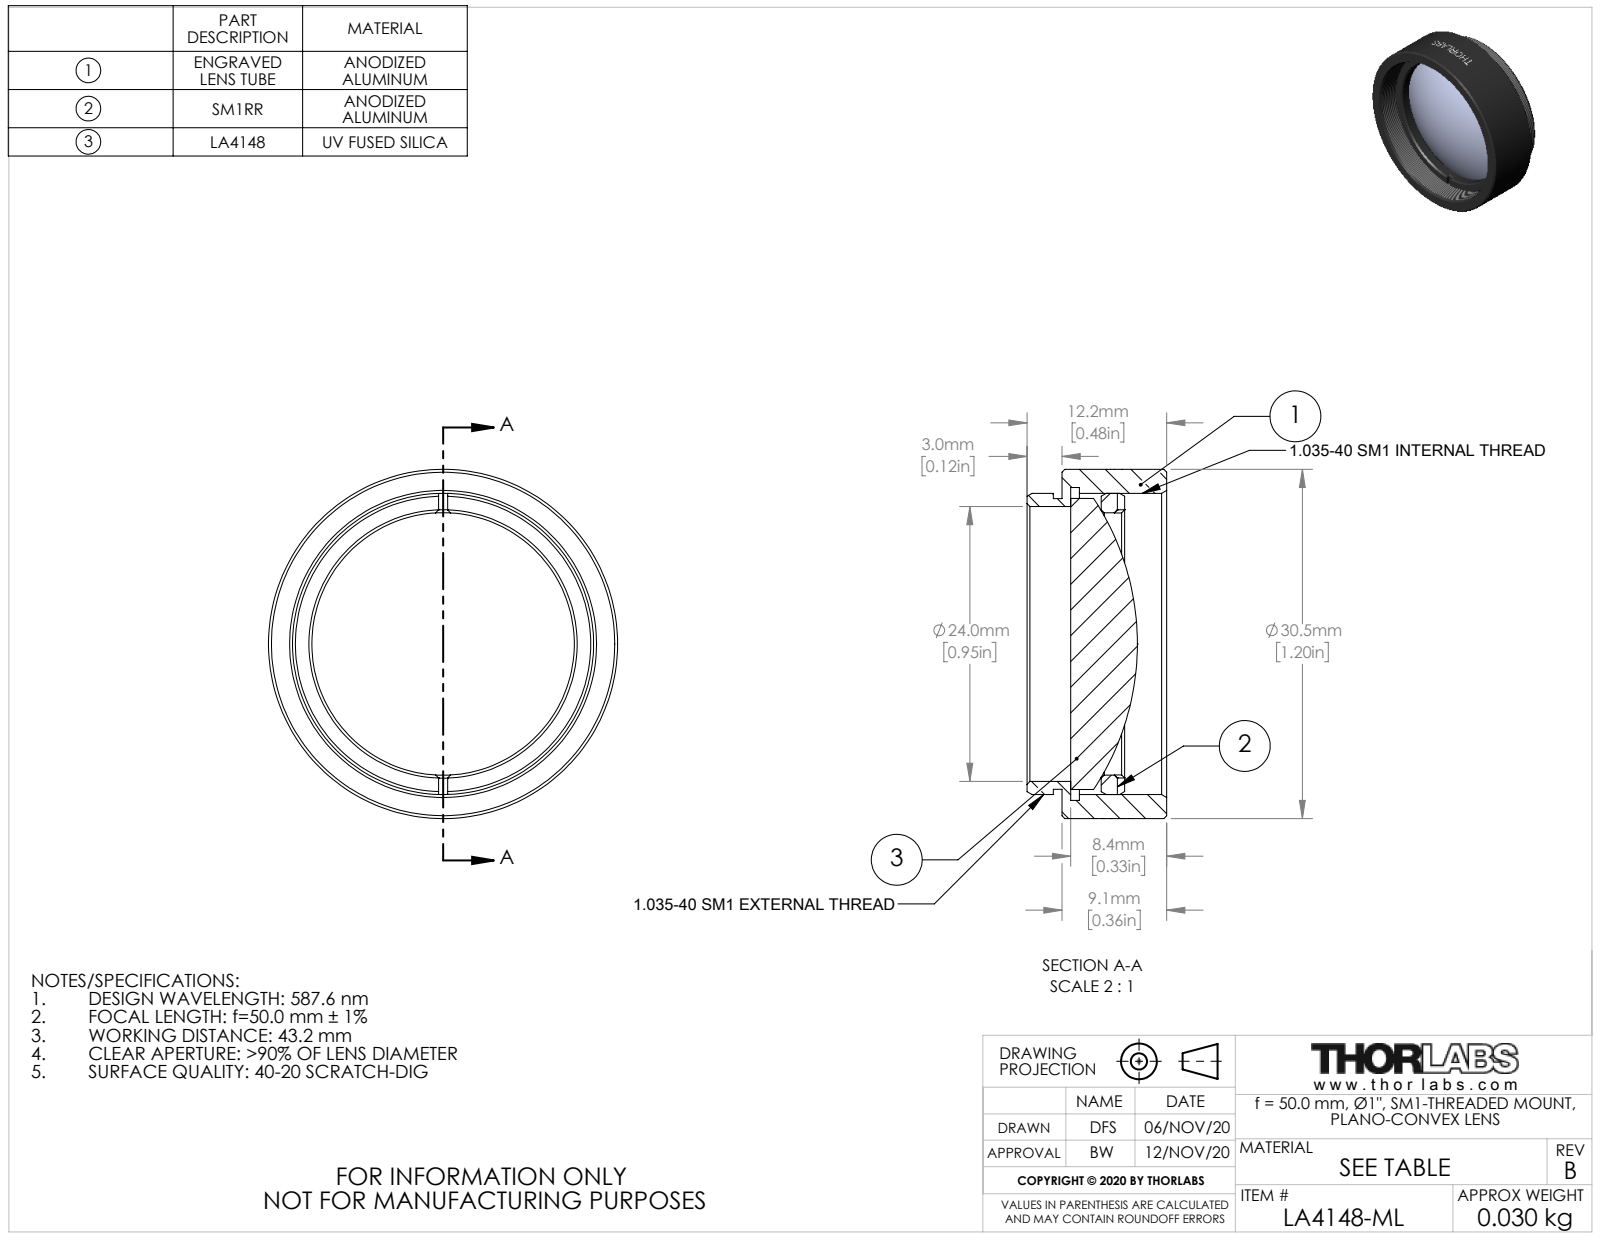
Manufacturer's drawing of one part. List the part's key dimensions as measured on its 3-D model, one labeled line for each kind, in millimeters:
Part name (STEP PRODUCT): 24452-E0W
STEP written by: SolidWorks 2018 (CONFIG_CONTROL_DESIGN)
Units: millimetres
Bodies: 3 solids, 117 faces (20 planar, 73 cylindrical, 24 other)
Overall size (bounding box): 30.48 × 30.48 × 12.19
Volume: 4 235 mm³ · Surface area: 4 494 mm²
Round holes (diameter × count): ⌀22.91 ×1, ⌀24 ×1, ⌀27.3 ×1
Round bosses / shafts (diameter × count): ⌀30.48 ×1, ⌀26.29 ×1, ⌀25.4 ×1, ⌀25.37 ×1
Main face-to-face distances: 0.76, 9.14, 8.38, 3.43, 2.67, 5.71, 5.46, 4.7, 2.03, 3.68
